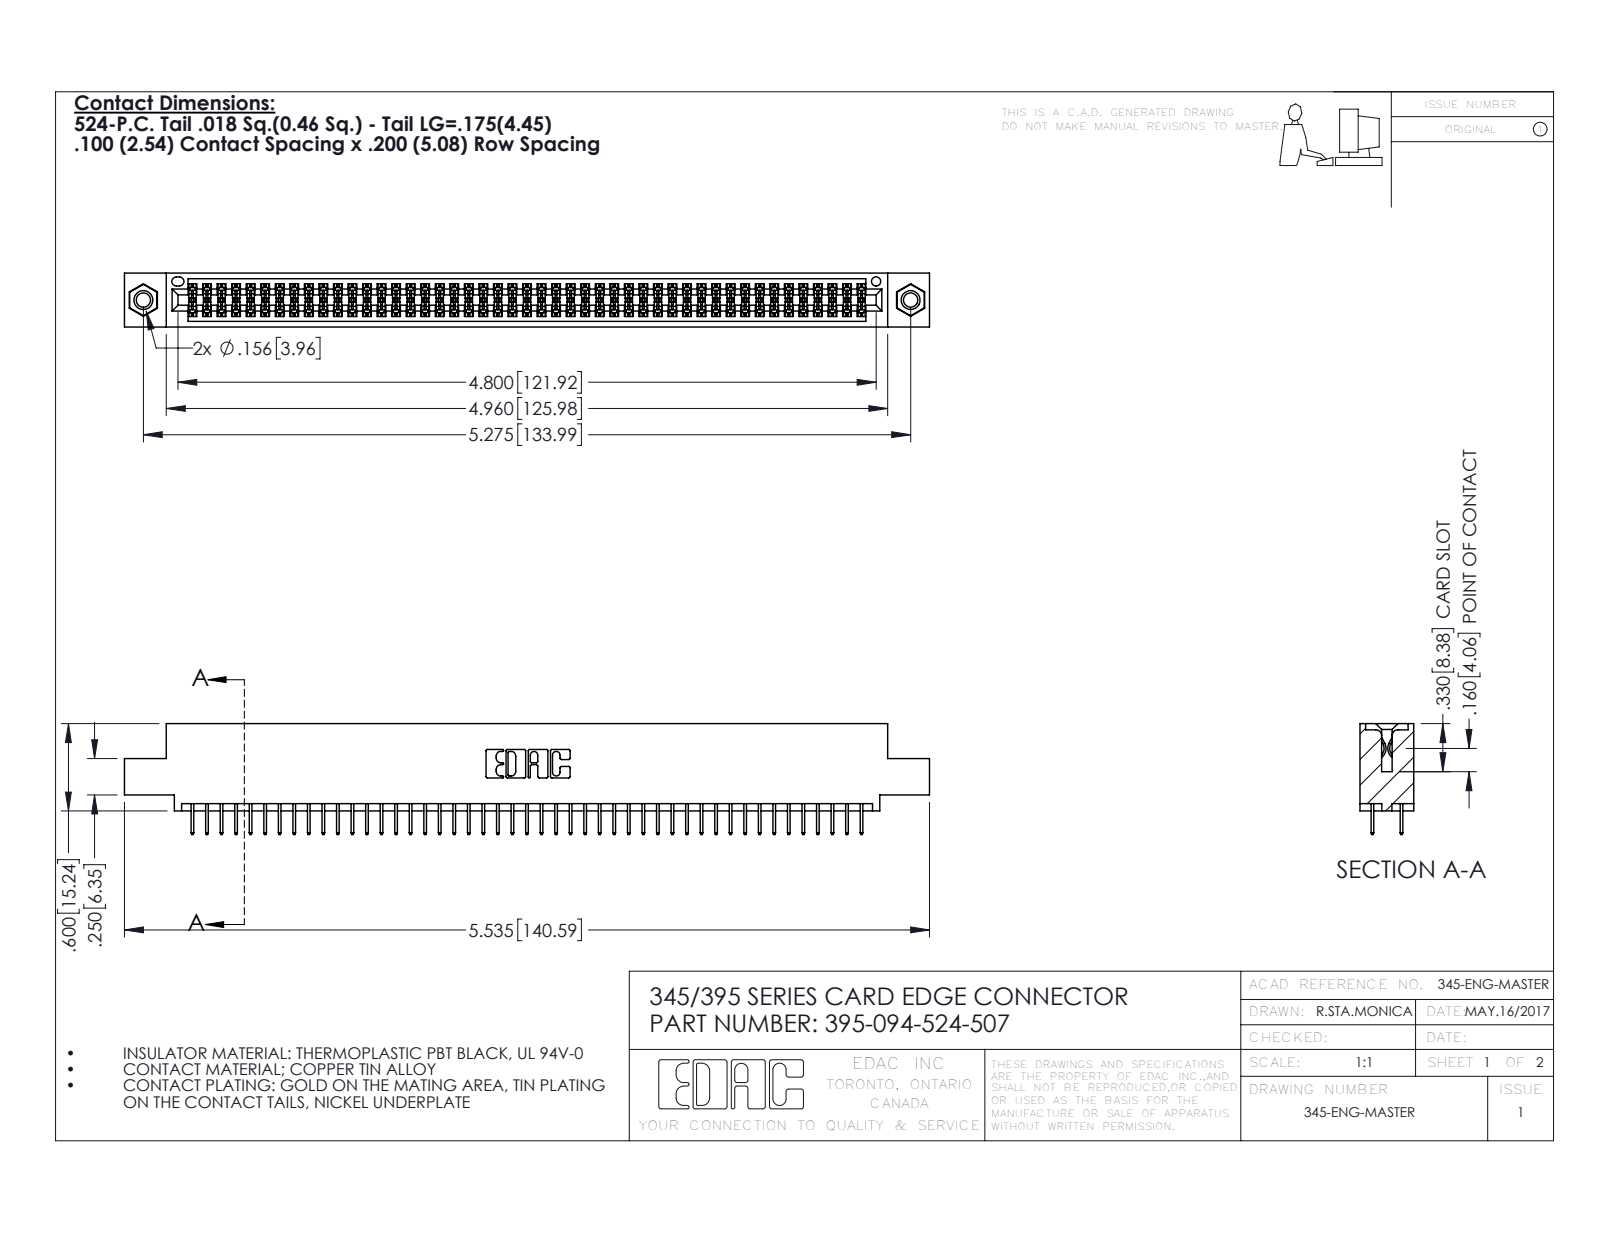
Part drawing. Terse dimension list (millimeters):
name: 345 Part_0.110 Offset - 0.156 Dia-TI; 345-250-001_345-250-005-103; 345-292-001_345-293-124; 395-094-524-507
written by: SolidWorks 2016 (CONFIG_CONTROL_DESIGN)
unit: mm
bodies: 97 solids, 5266 faces (3782 planar, 1468 cylindrical, 16 other)
size: 140.6 × 19.4 × 9.4
volume: 13 500 mm³; area: 19 760 mm²
holes: 2× ⌀2.5, 2× ⌀3.2, 2× ⌀4, 1× ⌀1.6
bosses: 2× ⌀3.9
rounds: 141× R0.2, 22× R0.3, 6× R0.2, 6× R0.8, 3× R0.7, 2× R0.4, 2× R0.5, 2× R0.6
face distances: 1.8, 7.6, 5.1, 9.4, 2.5, 6.9, 0.6, 5.7, 1.8, 4.4
hole spacings: 6.9, 128, 134
